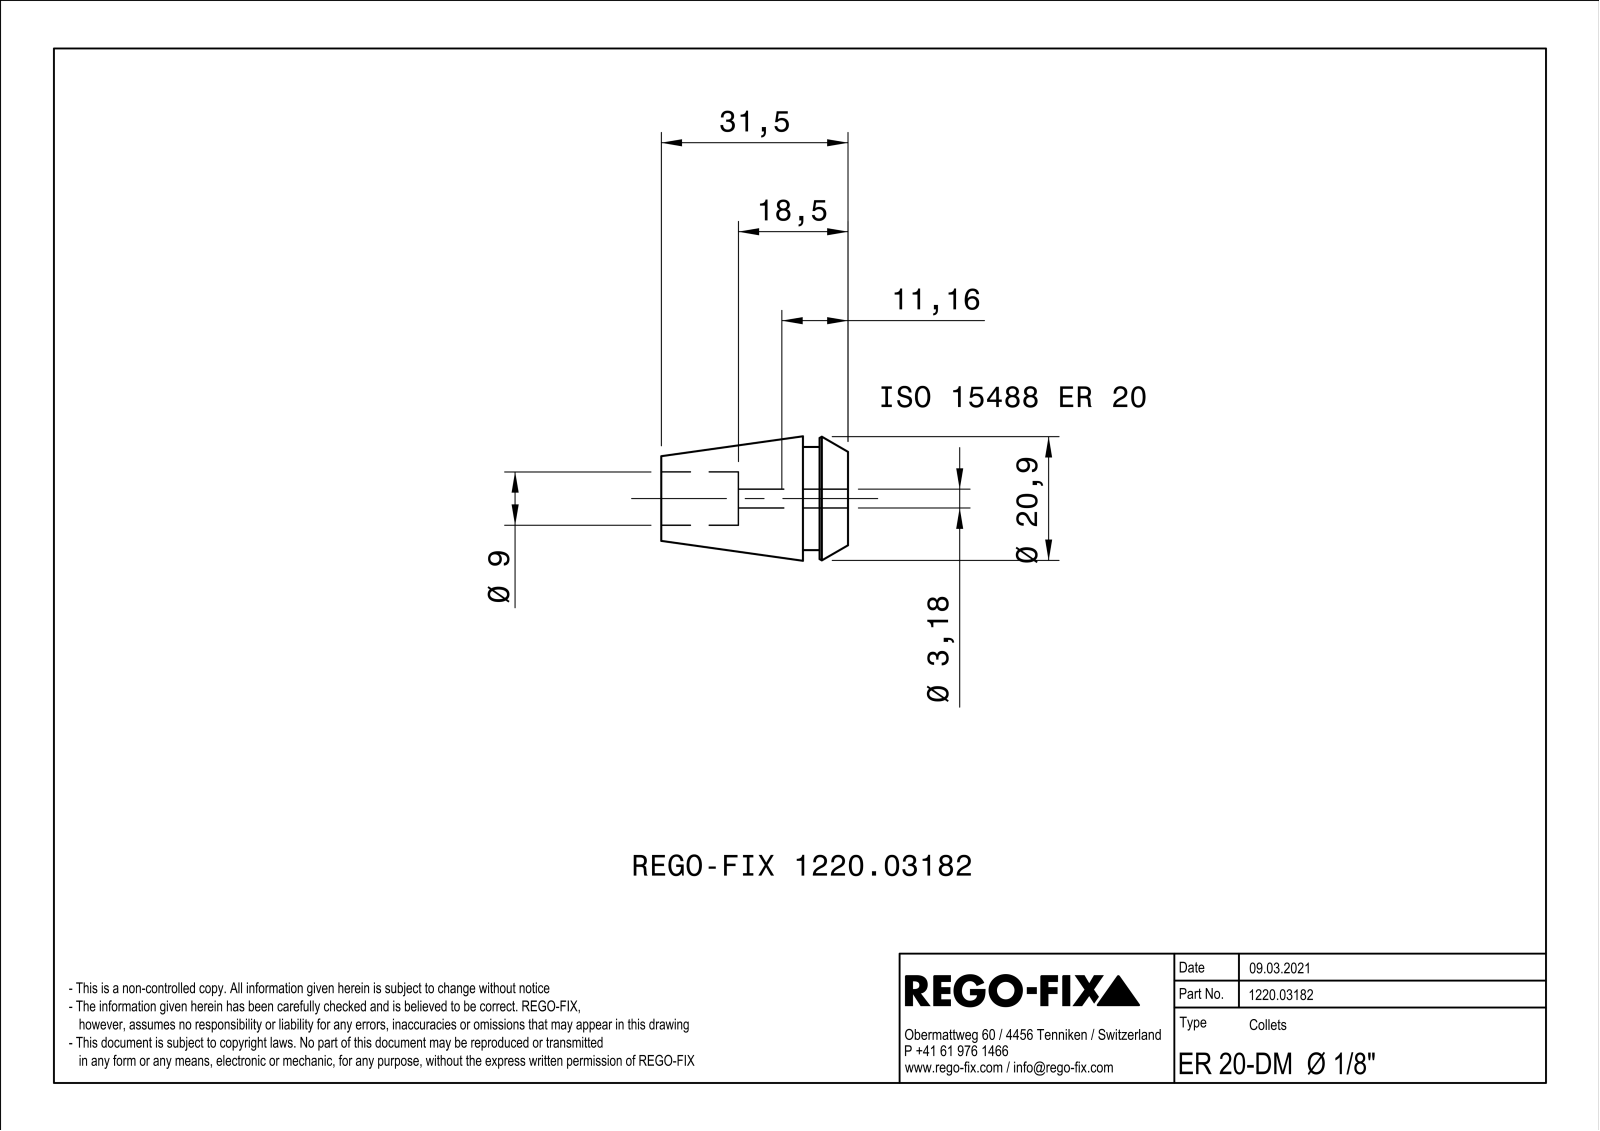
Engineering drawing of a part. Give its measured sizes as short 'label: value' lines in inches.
name: NOCUT
written by: SIEMENS PLM Software Solid Edge ST10 (AUTOMOTIVE_DESIGN)
unit: in
bodies: 1 solid, 94 faces (44 planar, 9 cylindrical, 41 other)
size: 1.24 × 0.811 × 0.811
volume: 0.354 in³; area: 6.786 in²
holes: 1× ⌀0.125, 1× ⌀0.354
bosses: 1× ⌀0.685
face distances: 0.02, 0.299, 0.189, 0.11, 1.24, 1.051, 0.941, 0.728, 0.539, 0.429
